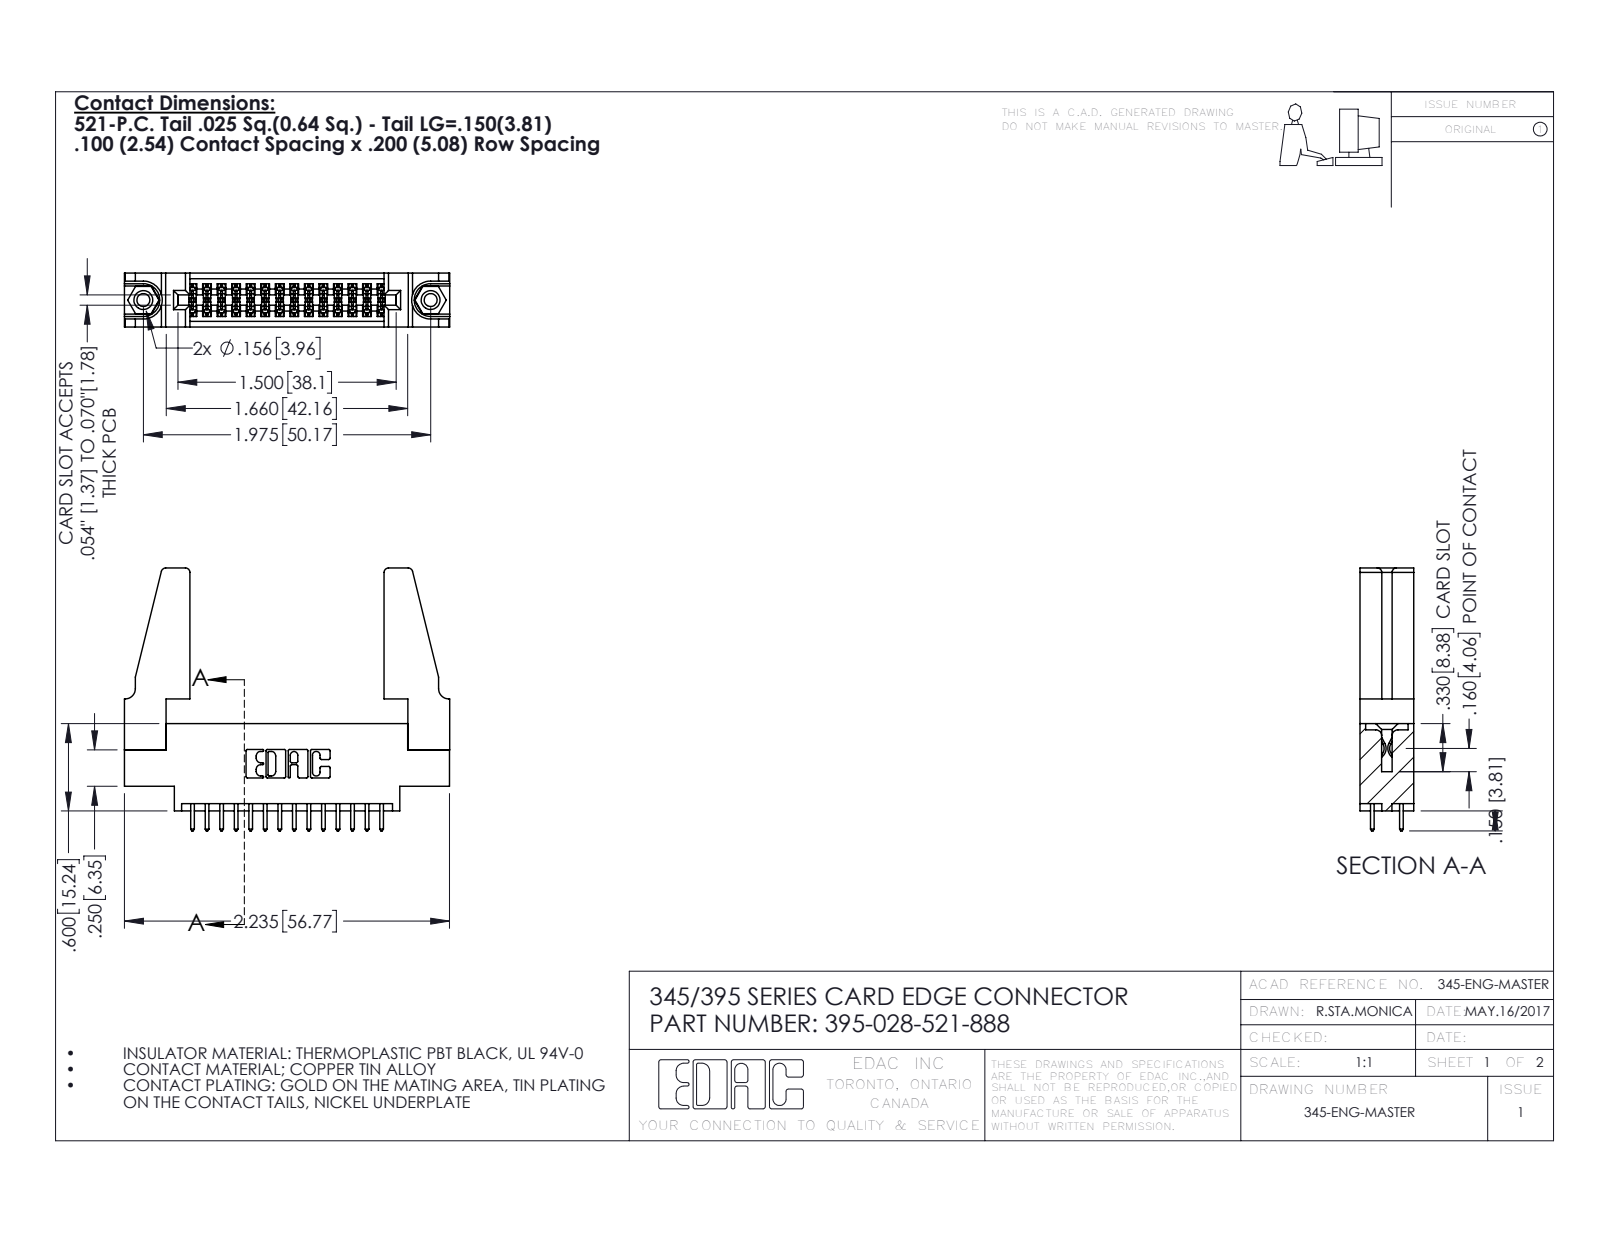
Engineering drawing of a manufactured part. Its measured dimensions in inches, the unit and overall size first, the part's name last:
Units: inches
Overall size (bounding box): 2.236 × 1.807 × 0.37
Round holes (diameter × count): ⌀0.089 ×2, ⌀0.125 ×2, ⌀0.156 ×2, ⌀0.064 ×1
Round bosses / shafts (diameter × count): ⌀0.155 ×2
Partial cylindrical surfaces — rounded edges, fillets, slot ends (radius × count): R0.006 ×42, R0.01 ×28, R0.01 ×22, R0.03 ×8, R0.007 ×6, R0.031 ×6, R0.026 ×3, R0.014 ×2
Main face-to-face distances: 0.37, 0.072, 0.298, 0.2, 0.098, 0.272, 0.025, 0.225, 0.175, 0.148
Hole centre spacings: 0.27, 1.742, 1.975
Volume: 0.512 in³ · Surface area: 15.86 in²
Bodies: 33 solids, 1654 faces (1080 planar, 558 cylindrical, 16 other)
Part name (STEP PRODUCT): 345-292-001_345-293-121; 395-028-521-888; 345-250-001_345-250-001-102; 345-220-078_345-220-088 (+1 more)
STEP written by: SolidWorks 2016 (CONFIG_CONTROL_DESIGN)
